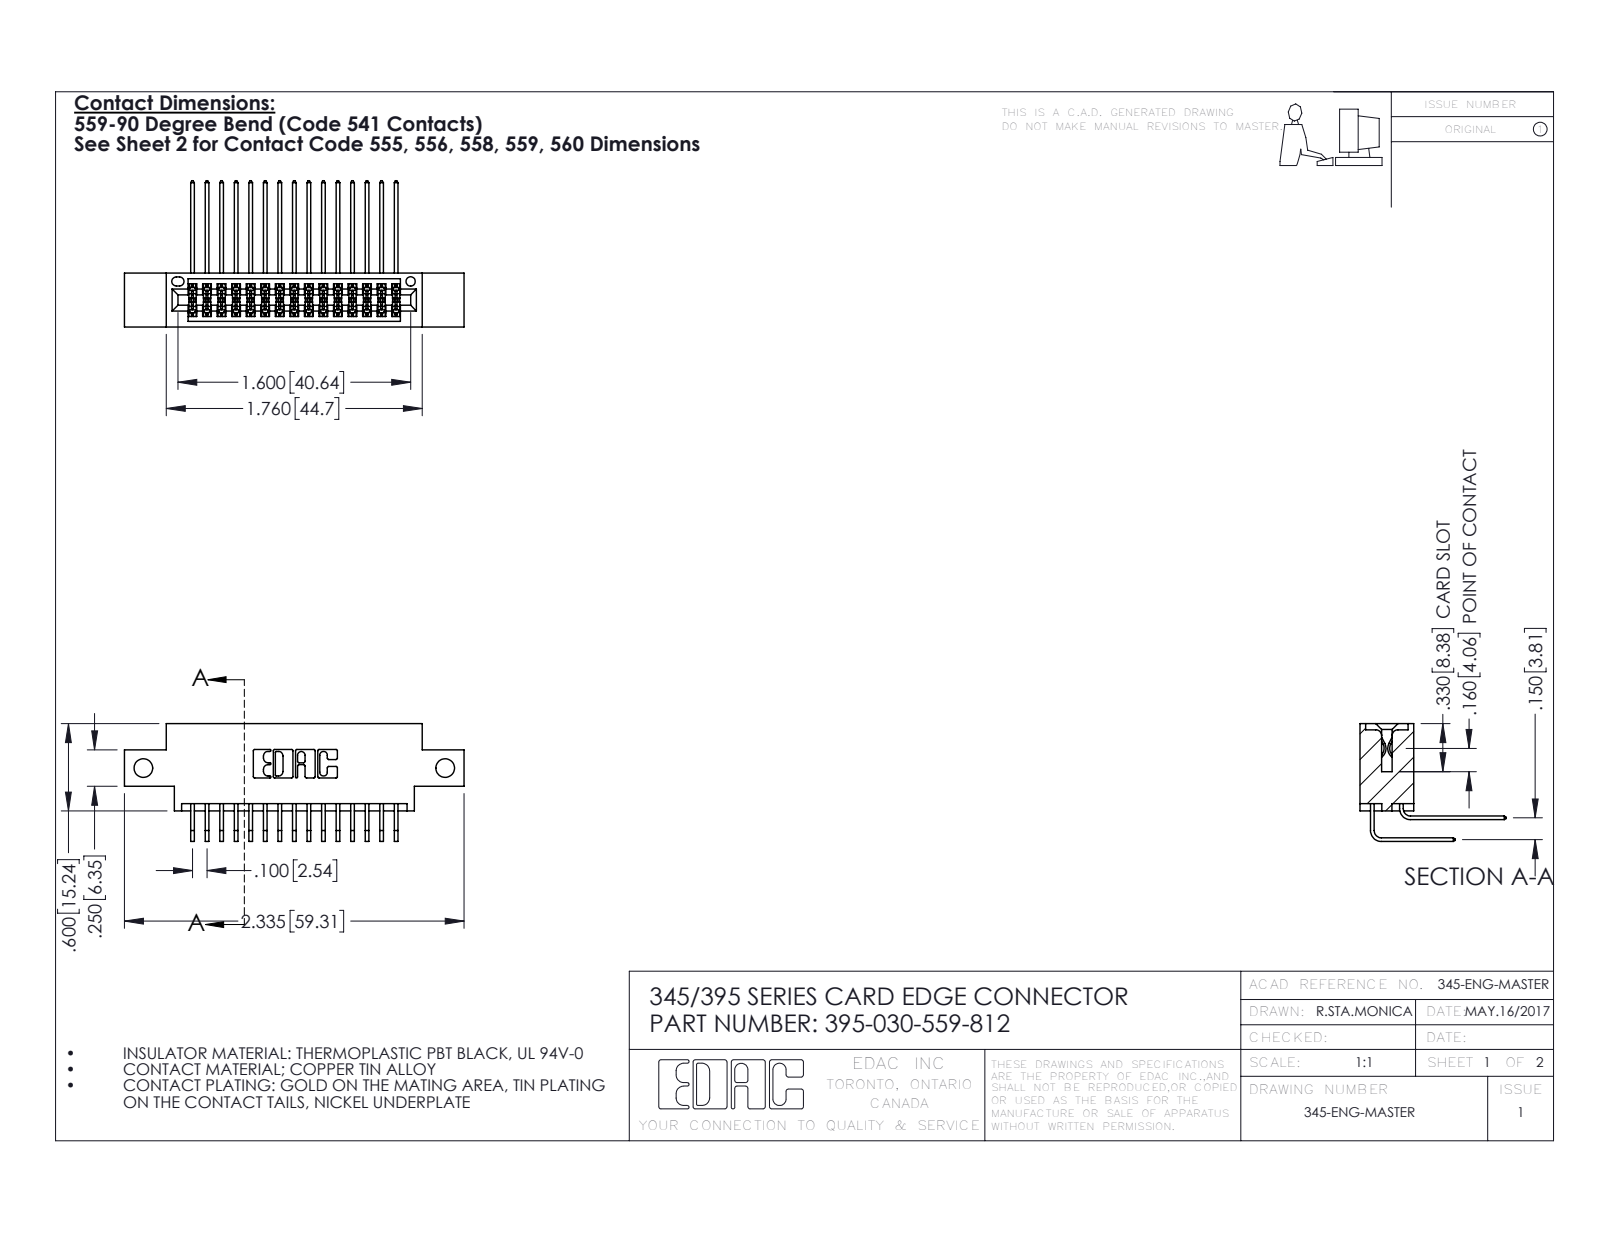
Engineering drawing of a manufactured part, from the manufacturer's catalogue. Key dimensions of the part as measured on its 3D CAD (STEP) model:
Part name (STEP PRODUCT): 345-292-001_559 Tail - 2; 395-030-559-812; 345 Part_0.170 Offset - Side Mount; 345-292-001_558 559 Tail - 1
STEP written by: SolidWorks 2016 (CONFIG_CONTROL_DESIGN)
Units: inches
Bodies: 31 solids, 1690 faces (1134 planar, 556 cylindrical, 0 other)
Overall size (bounding box): 2.335 × 1.005 × 0.809
Volume: 0.335 in³ · Surface area: 13.03 in²
Round holes (diameter × count): ⌀0.128 ×2, ⌀0.064 ×1
Partial cylindrical surfaces — rounded edges, fillets, slot ends (radius × count): R0.006 ×45, R0.01 ×22, R0.007 ×6, R0.031 ×6, R0.026 ×3, R0.014 ×2, R0.019 ×2, R0.022 ×2
Main face-to-face distances: 0.072, 0.298, 0.37, 0.2, 0.098, 0.272, 0.025, 0.15, 0.225, 0.175
Hole centre spacings: 2.075
